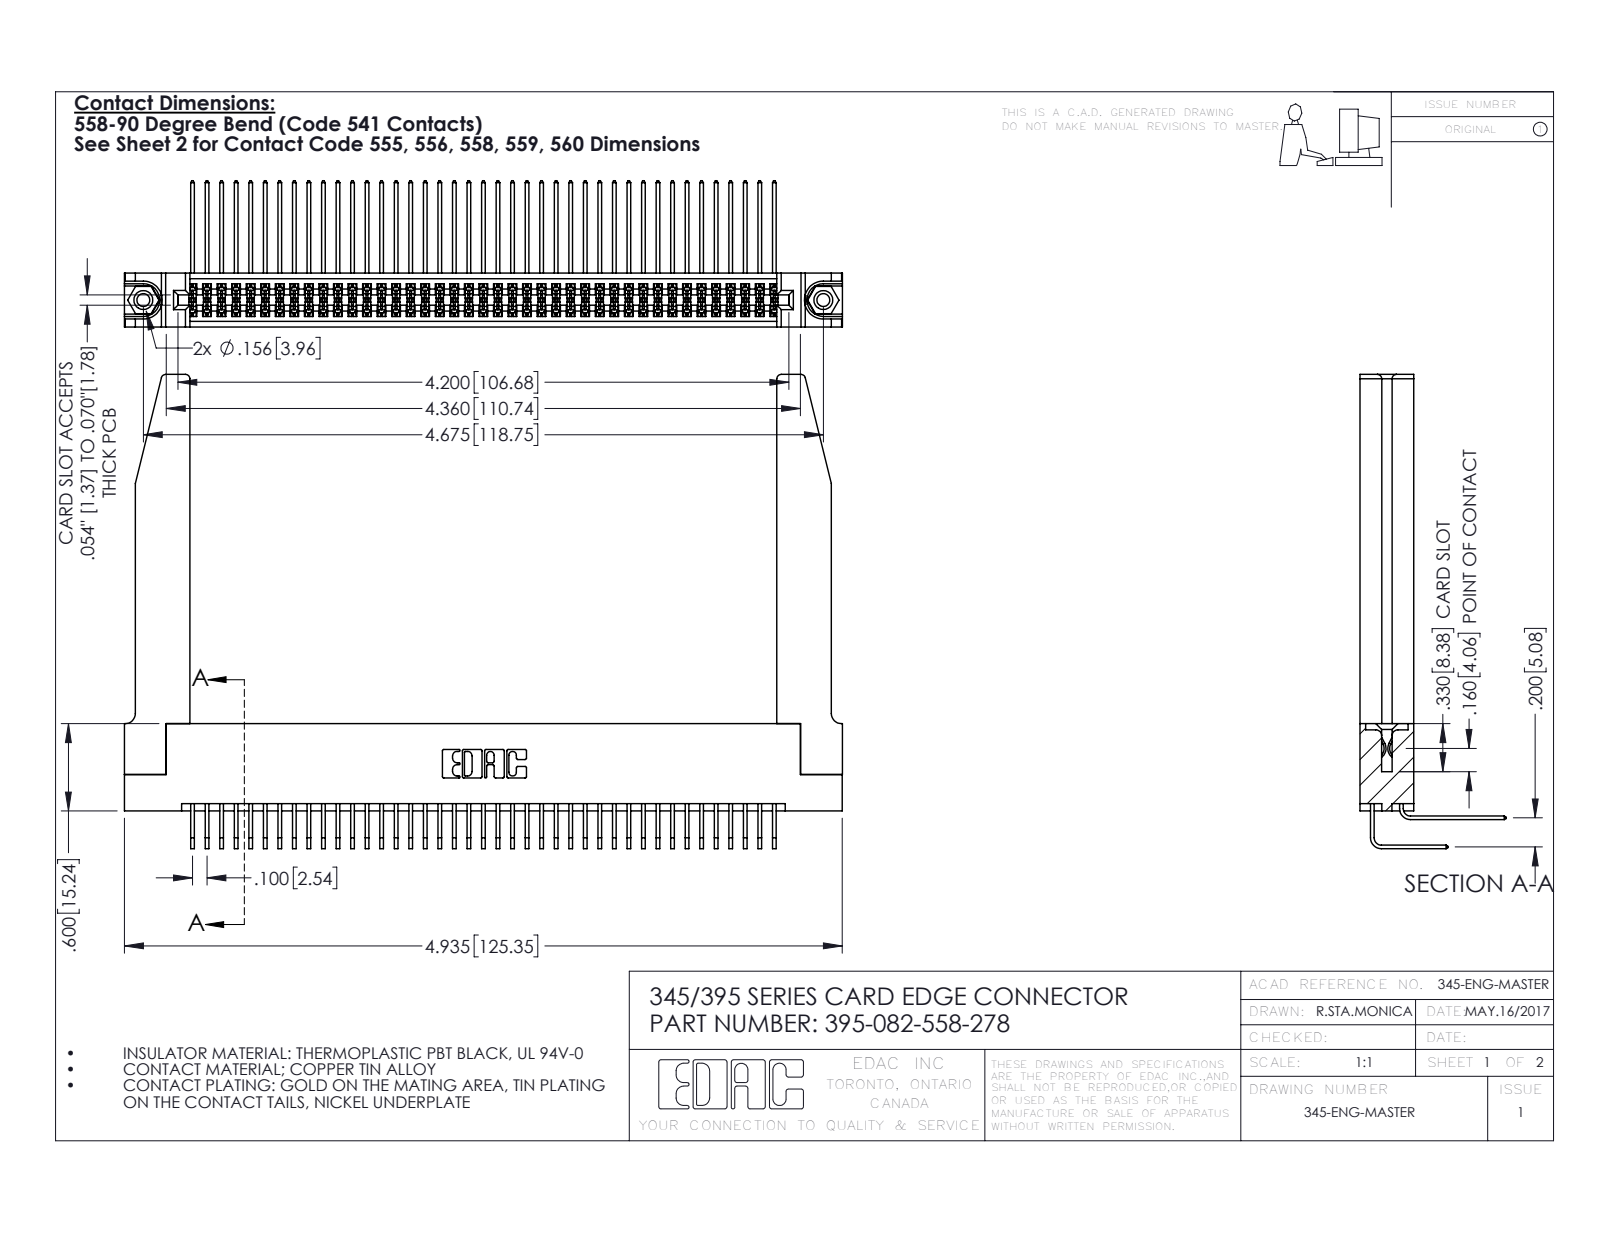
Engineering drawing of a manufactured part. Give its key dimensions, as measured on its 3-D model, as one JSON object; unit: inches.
{"part_name": "345-220-078_345-220-078; 345-292-001_558 Tail - 2; 345-292-001_558 559 Tail - 1; 345 Part_Flush Mounting Lugs - 0.156 Dia-TH (+2 more)", "step_written_by": "SolidWorks 2016 (CONFIG_CONTROL_DESIGN)", "units": "inches", "bodies": {"solids": 87, "faces": 4624, "planar": 3092, "cylindrical": 1480, "other": 52}, "overall_size": [4.936, 3.259, 1.005], "volume_in3": 1.246, "surface_area_in2": 42.98, "round_holes": [[0.089, 2], [0.125, 2], [0.156, 2], [0.064, 1]], "round_bosses_or_shafts": [[0.155, 2]], "partial_cylinders_radius": [[0.006, 124], [0.01, 22], [0.03, 8], [0.007, 6], [0.031, 6], [0.026, 3], [0.014, 2], [0.019, 2]], "face_to_face_distances": [0.072, 0.37, 0.298, 0.2, 0.098, 0.272, 0.025, 0.225, 0.285, 0.148], "hole_center_spacings": [0.27, 4.439, 4.675]}
